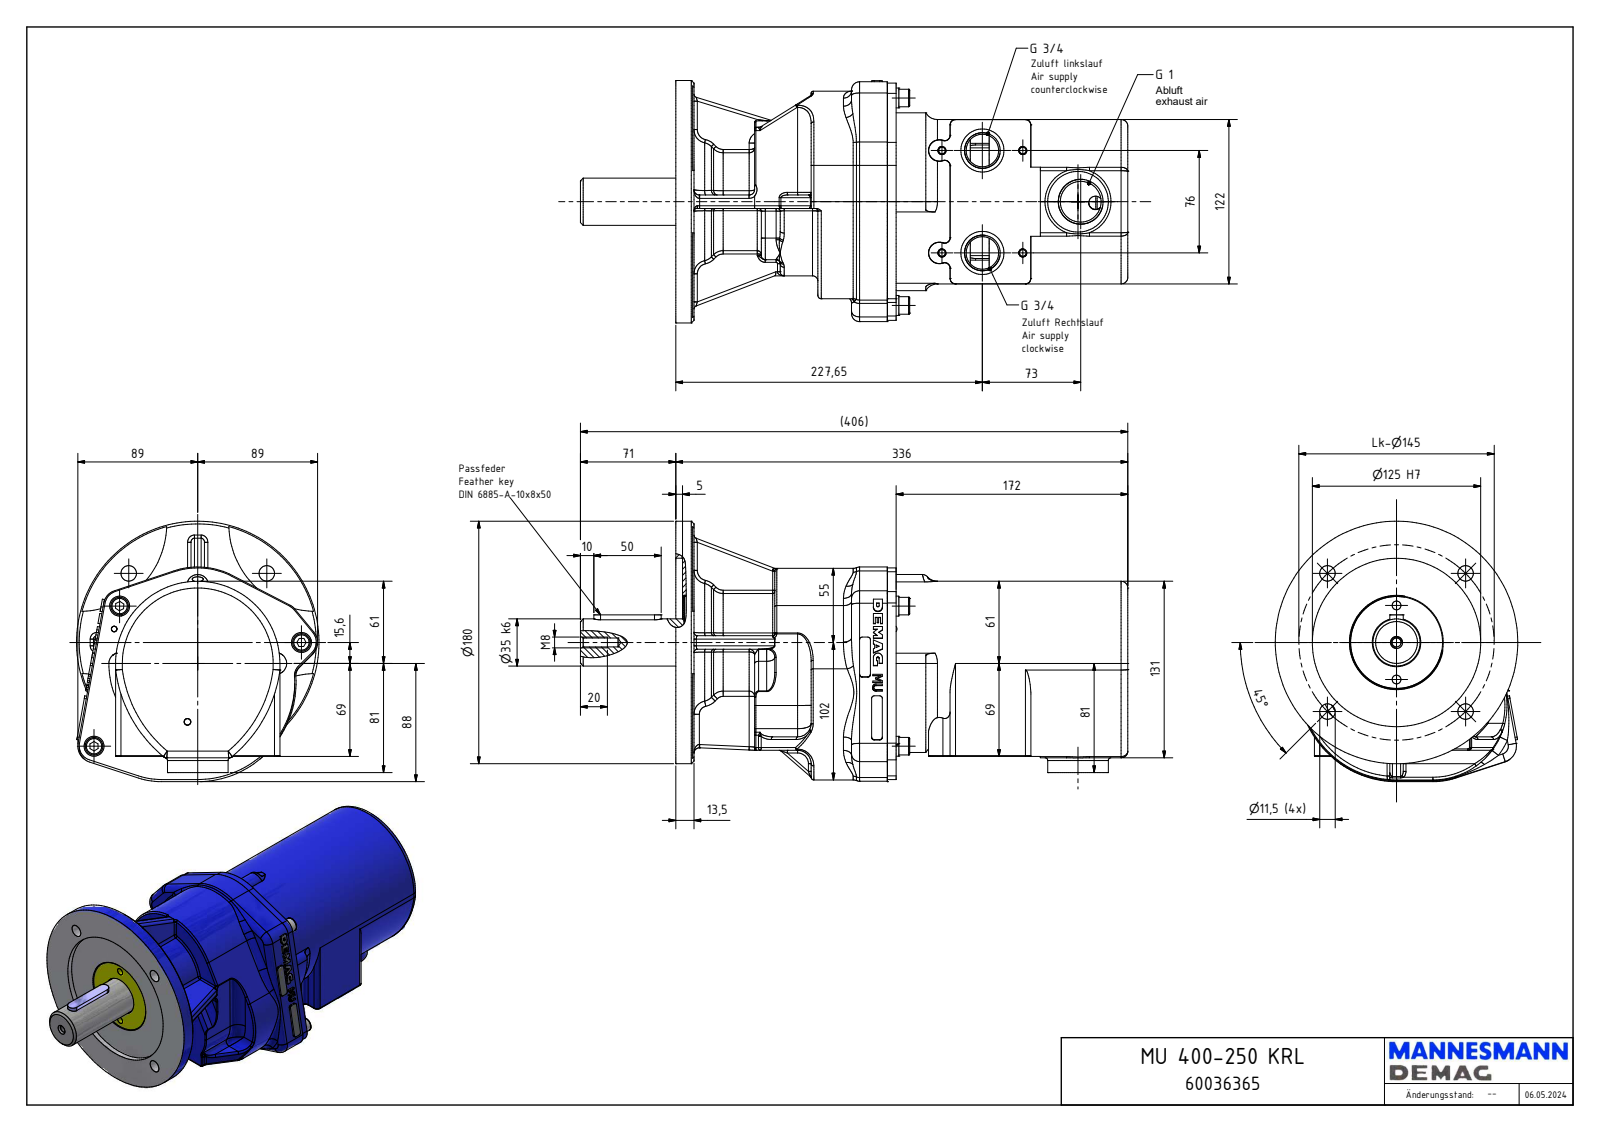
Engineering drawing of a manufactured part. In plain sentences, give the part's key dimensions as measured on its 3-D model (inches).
The part is named "MU 400-250 KRL_60036365". Its 3-D file was written by "Autodesk Inventor 2021 (AUTOMOTIVE_DESIGN)". It is 2 solids with 783 faces: 275 planar, 256 cylindrical and 252 other. Overall it measures 16.012 by 7.598 by 7.087 inches. Its volume is 282 cubic inches and its surface area 410 square inches. Round holes: 6 of diameter 0.374, 4 of diameter 0.194, 4 of diameter 0.262, 4 of diameter 0.453, 3 of diameter 0.335, 2 of diameter 0.197, 2 of diameter 0.256, 2 of diameter 0.95, 2 of diameter 1.26, 1 of diameter 0.098, 1 of diameter 0.11, 1 of diameter 0.154. Round bosses or shafts: 3 of diameter 0.583, 3 of diameter 0.512, 3 of diameter 0.315, 1 of diameter 7.087, 1 of diameter 4.803, 1 of diameter 1.772, 1 of diameter 1.378, 1 of diameter 0.63. Partial cylindrical surfaces (rounded edges, fillets, slot ends): 28 of radius 0.079, 20 of radius 0.098, 18 of radius 0.157, 12 of radius 0.236, 12 of radius 0.433, 8 of radius 0.118, 7 of radius 2.165, 6 of radius 0.039. The main face-to-face distances are 0.039, 13.224, 0.197, 0.295, 13.028, 6.772, 6.256, 6.453, 12.693, 5.921. The hole center spacings are 1.181, 2.126, 2.225, 2.855, 3.217, 3.7, 4.037, 5.151.
